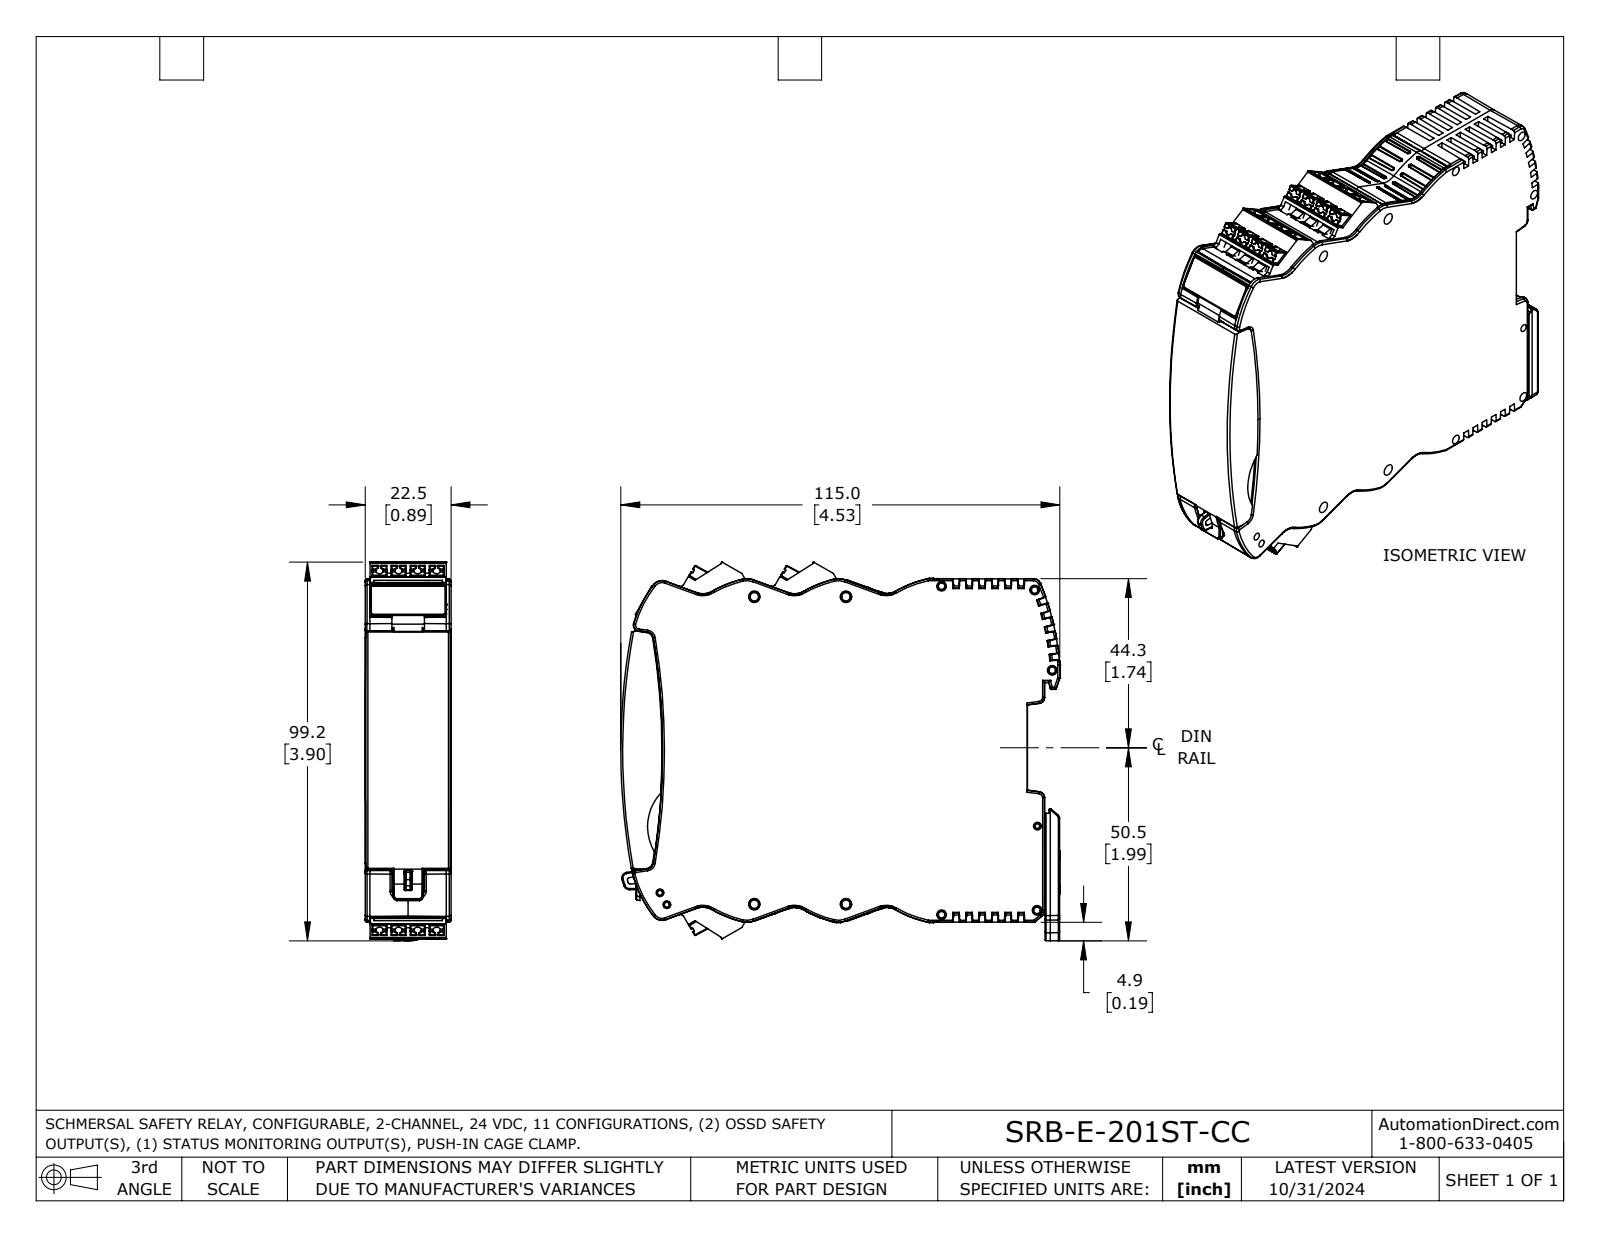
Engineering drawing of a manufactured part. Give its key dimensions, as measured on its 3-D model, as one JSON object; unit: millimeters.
{"part_name": "SRB-E-201ST-CC_REV1", "step_written_by": "SolidWorks 2023 (AUTOMOTIVE_DESIGN)", "units": "millimeters", "bodies": {"solids": 2, "faces": 4072, "planar": 1995, "cylindrical": 1156, "other": 921}, "overall_size": [115, 99.2, 22.5], "volume_mm3": 210700, "surface_area_mm2": 42370, "round_holes": [[1.8, 1]], "round_bosses_or_shafts": [[1.7, 1]], "partial_cylinders_radius": [[0.3, 217], [0.2, 182], [0.5, 177], [0.3, 84], [0.1, 33], [1, 28], [1.5, 26], [1.2, 12]], "face_to_face_distances": [22.5, 3.4, 0.9, 6.8, 3.4, 21.6, 4.5, 1.3, 21.2, 0.4]}
